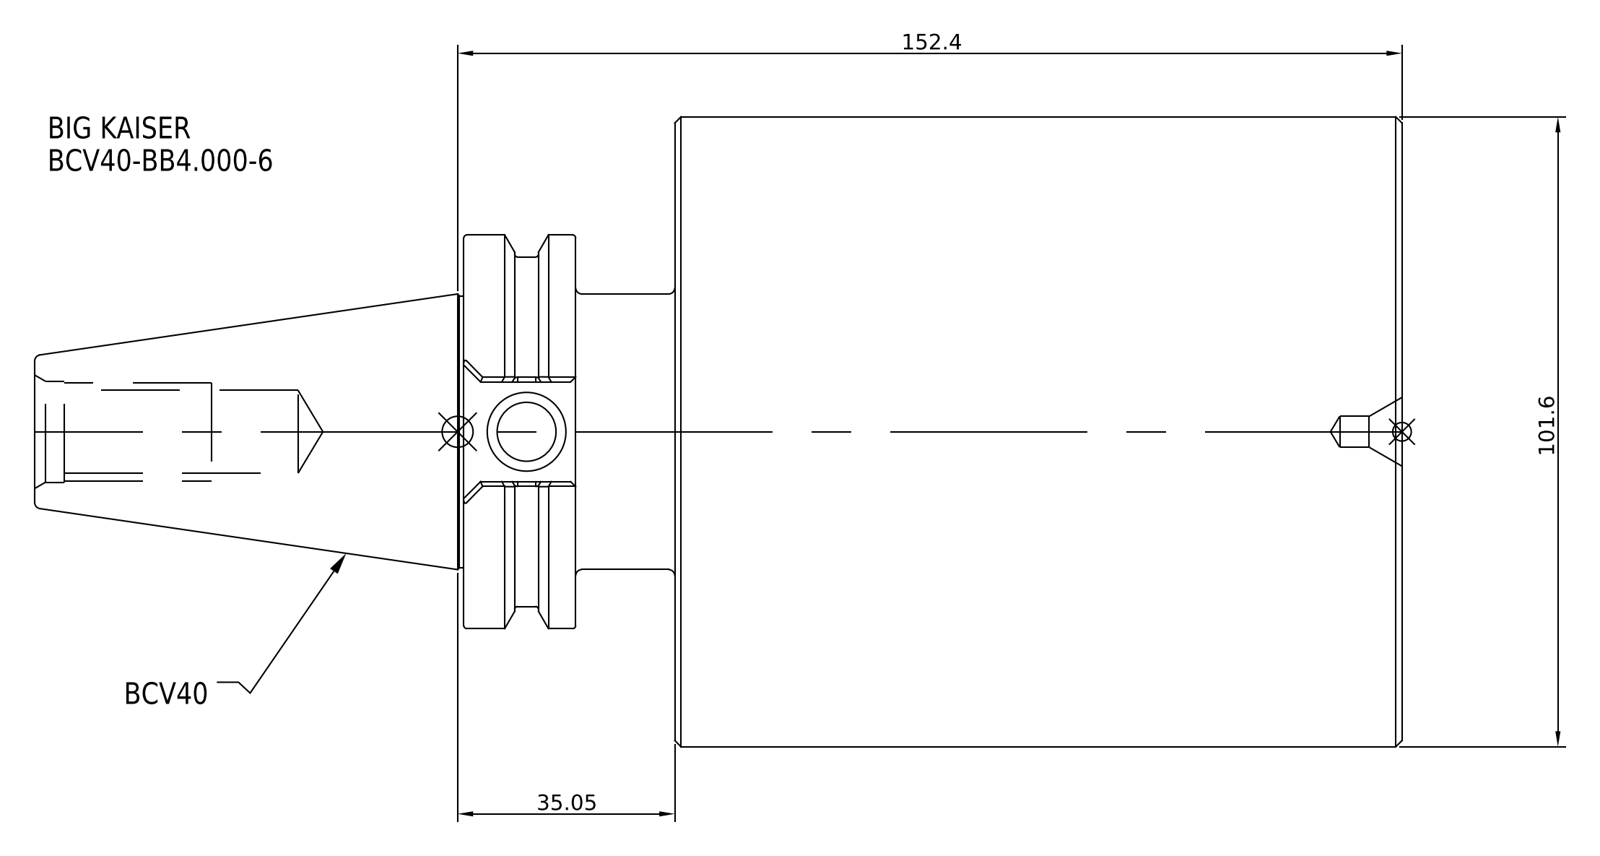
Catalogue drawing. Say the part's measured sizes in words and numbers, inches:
The part is named "BVC40_BB4.000_6". Its 3-D file was written by "SolidWorks 2021 (CONFIG_CONTROL_DESIGN)". It is 1 solid with 16 faces: 7 planar, 6 cylindrical and 3 other. Overall it measures 8.687 by 4 by 4 inches. Its volume is 66.94 cubic inches and its surface area 108.6 square inches. Round bosses or shafts: 1 of diameter 4, 1 of diameter 2.5, 1 of diameter 2.219, 1 of diameter 1.75. The main face-to-face distances are 4.62, 5.961, 1.341, 5.25, 0.63, 0.711, 8.687, 4.067, 3.437, 2.726.
